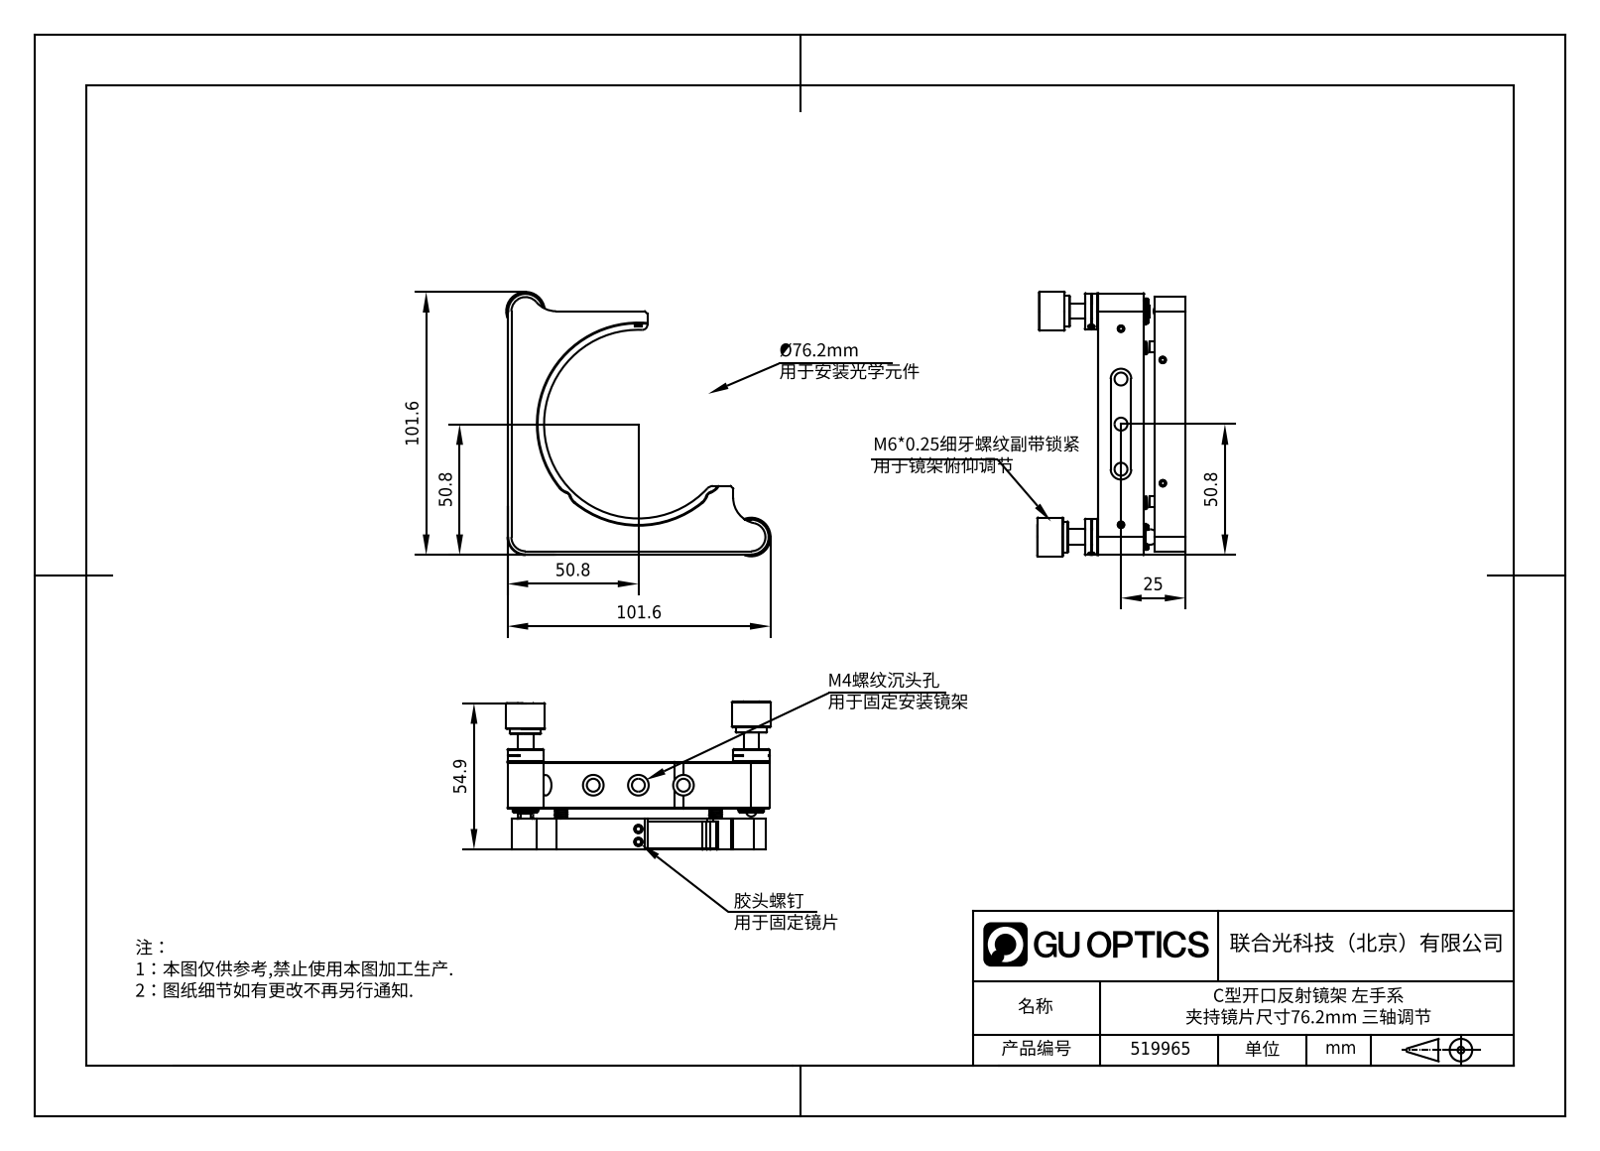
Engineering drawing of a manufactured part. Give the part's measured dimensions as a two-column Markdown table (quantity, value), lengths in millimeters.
| quantity | value |
| --- | --- |
| part name | 519965 |
| STEP written by | SolidWorks 2020 (CONFIG_CONTROL_DESIGN) |
| units | millimeters |
| bodies | 0 solids, 1106 faces (648 planar, 324 cylindrical, 134 other) |
| overall size | 101.6 × 101.6 × 50.5 |
| round holes (diameter × count) | 9.5 × 3, 10 × 3, 14 × 3 |
| round bosses / shafts (diameter × count) | 4 × 8, 6 × 7, 10 × 6, 5 × 6, 2 × 4, 1.5 × 4, 10.5 × 3, 8 × 3 |
| partial cylindrical surfaces (radius × count) | 1.1 × 8, 2.5 × 7, 0.8 × 4, 1.25 × 4, 1.5 × 4, 3.5 × 4, 6 × 4, 5.25 × 3 |
| main face-to-face distances | 12, 21.5, 33.5, 15.5, 3.5, 18, 2, 14, 2.25, 2.75 |
| hole center spacings | 87.6, 123.89 |
